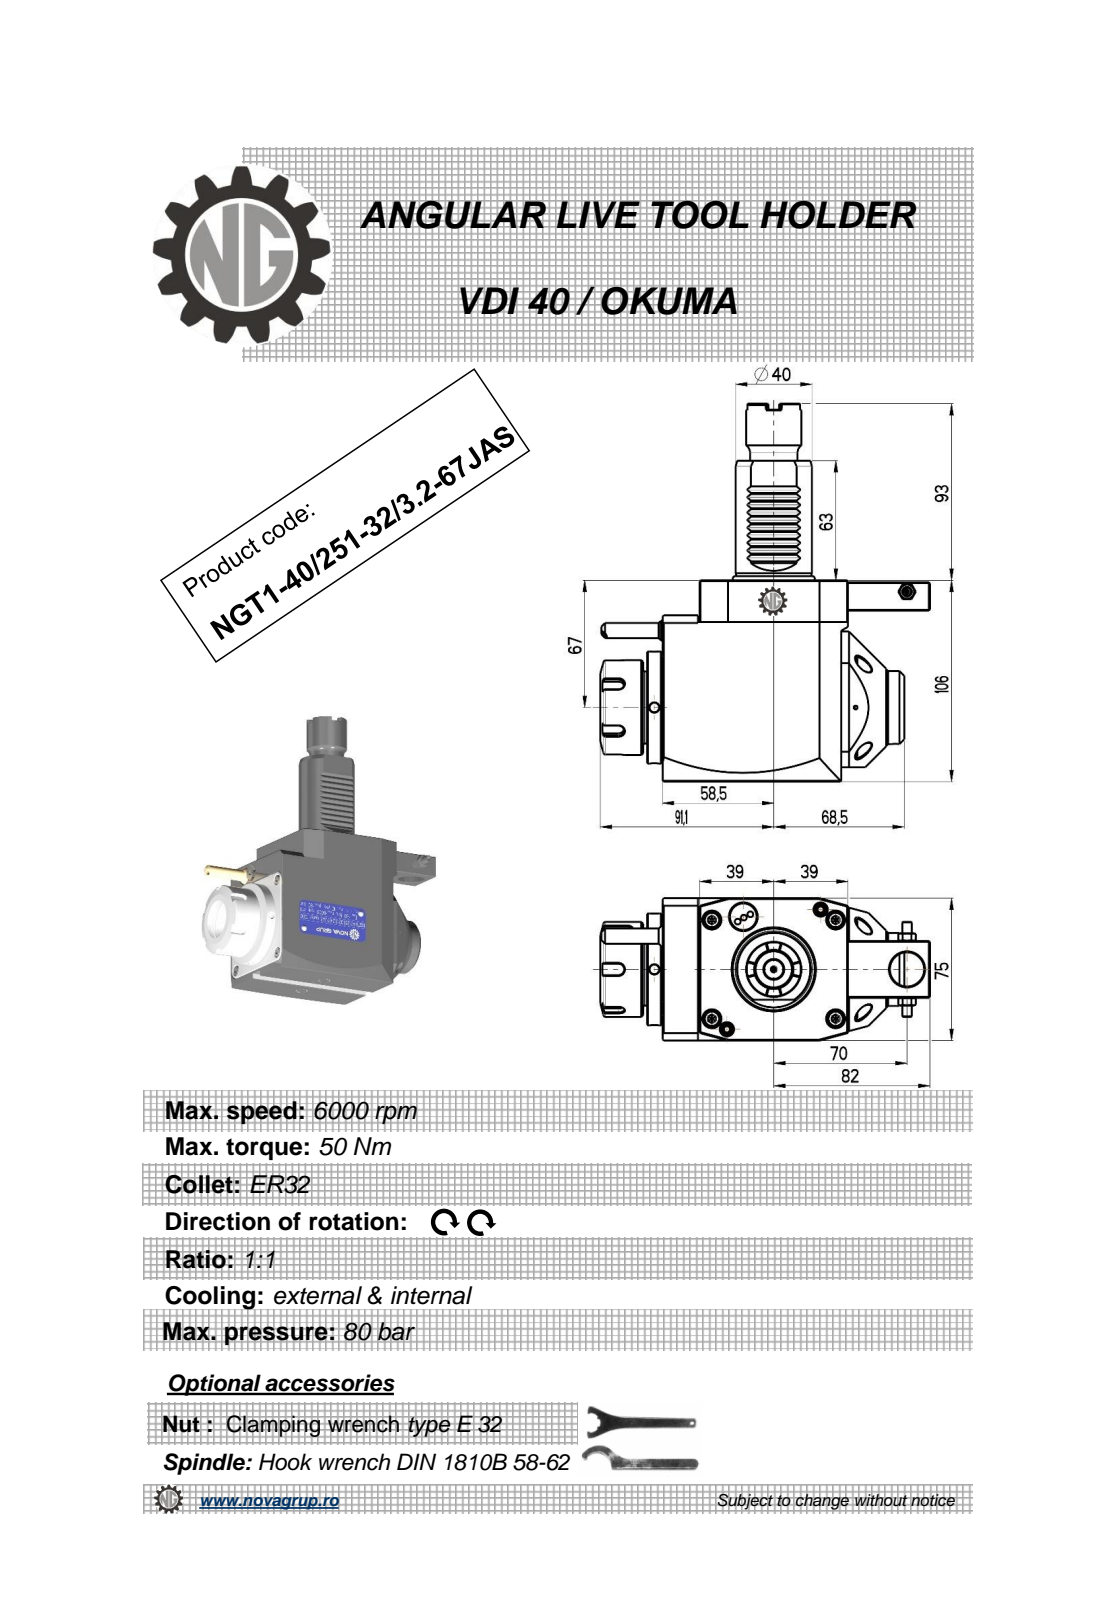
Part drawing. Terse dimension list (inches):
name: NGT1_40_251_32_3_2_67JAS
written by: PRO/ENGINEER BY PARAMETRIC TECHNOLOGY CORPORATION, 2010280 (CONFIG_CONTROL_DESIGN)
unit: in
bodies: 1 solid, 502 faces (226 planar, 101 cylindrical, 175 other)
size: 7.835 × 6.815 × 2.953
volume: 59.13 in³; area: 124.6 in²
holes: 3× ⌀0.197, 1× ⌀0.118, 1× ⌀0.165, 1× ⌀0.374, 1× ⌀0.709, 1× ⌀1.063
bosses: 1× ⌀2.323, 1× ⌀1.969, 1× ⌀1.85, 1× ⌀1.614, 1× ⌀1.575, 1× ⌀1.516, 1× ⌀1.142, 1× ⌀0.984
rounds: 12× R0.01, 10× R0.012, 6× R0.008, 5× R0.118, 3× R0.236, 2× R0.228, 2× R23.622, 1× R0.394
face distances: 2.953, 4.173, 4.016, 0.138, 1.083, 0.039, 3.839, 0.787, 0.768, 0.315
hole spacings: 1.017, 1.737, 2.343, 5.226, 5.752
